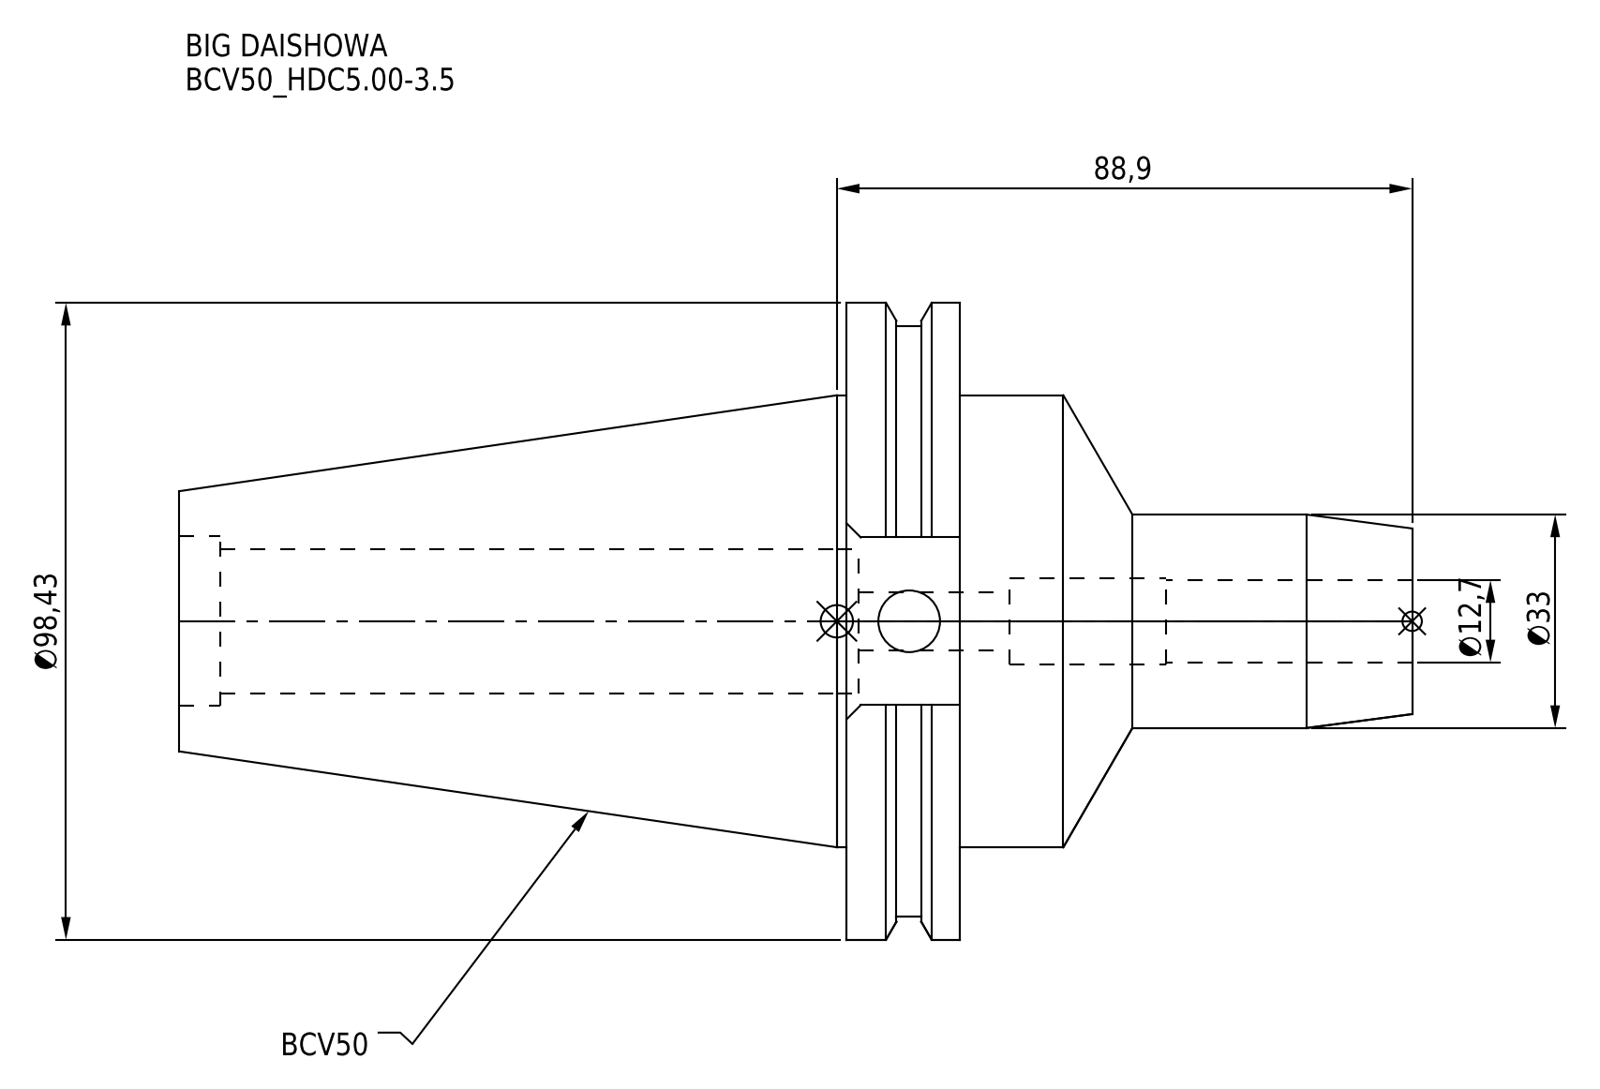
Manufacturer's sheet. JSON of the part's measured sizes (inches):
{"part_name": "BCV50_HDC_500-3_5", "step_written_by": "CREO PARAMETRIC BY PTC INC, 2016380 (AUTOMOTIVE_DESIGN)", "units": "inches", "bodies": {"solids": 1, "faces": 59, "planar": 23, "cylindrical": 26, "other": 10}, "overall_size": [7.5, 3.875, 3.738], "volume_in3": 26.79, "surface_area_in2": 85.62, "round_holes": [[0.354, 1], [0.375, 1], [0.5, 1], [0.52, 1], [0.878, 1], [1.033, 1]], "round_bosses_or_shafts": [[3.875, 1], [3.594, 1], [2.75, 1], [1.299, 1]], "face_to_face_distances": [0.691, 4.75, 4.059, 2.75, 3.441, 7.5, 2.872, 3.366, 0.616, 0.075]}
